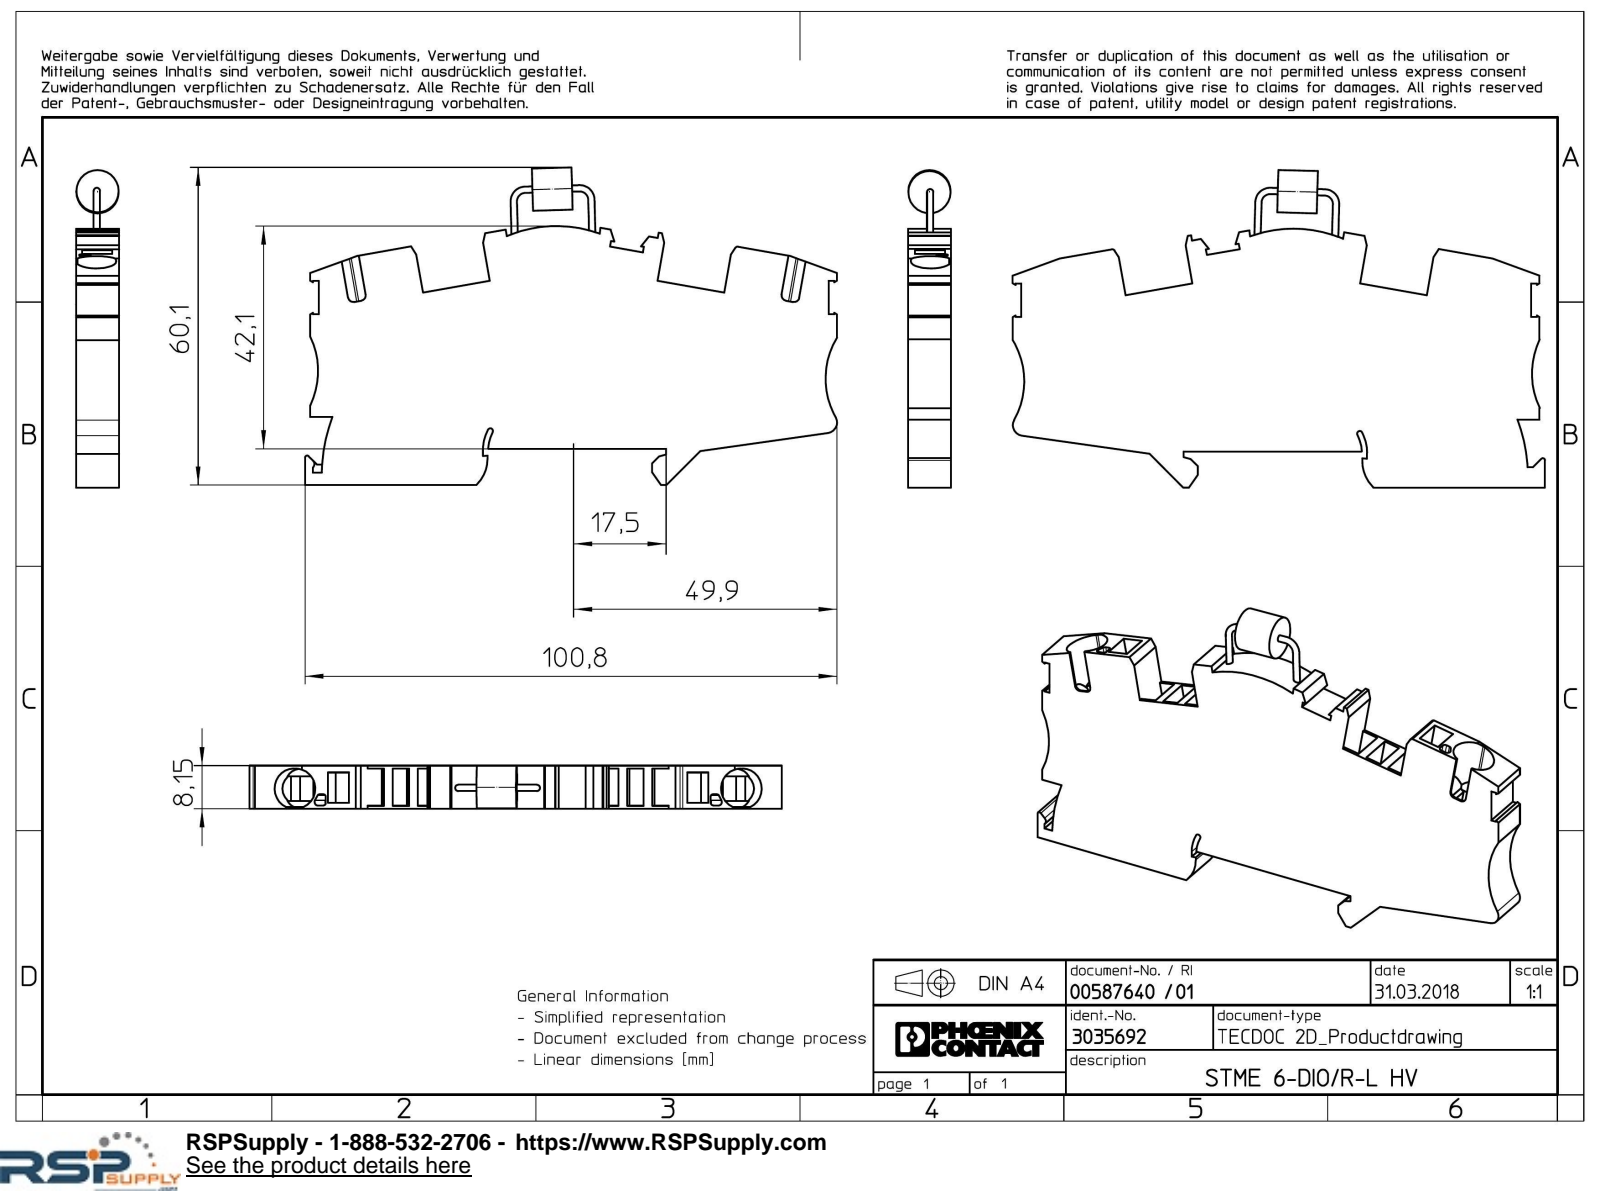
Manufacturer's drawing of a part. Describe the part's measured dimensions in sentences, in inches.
The part is named "STME-6-DIO_R-L-Select". Its 3-D file was written by "Creo Elements/Direct Modeling 18.1I 14-Aug-2016 (C) Parametric Technology GmbH (AUTOMOTIVE_DESIGN)". It is 1 solid with 184 faces: 147 planar, 33 cylindrical and 4 other. Overall it measures 3.969 by 2.366 by 0.321 inches. Its volume is 1.649 cubic inches and its surface area 21.9 square inches. Round bosses or shafts: 1 of diameter 0.315. Partial cylindrical surfaces (rounded edges, fillets, slot ends): 7 of radius 0.02, 4 of radius 0.039, 4 of radius 0.15, 2 of radius 0.026, 2 of radius 0.591, 2 of radius 0.945, 1 of radius 0.016, 1 of radius 0.024. The main face-to-face distances are 0.321, 0.191, 0.124, 0.067, 0.276, 0.022, 0.27, 0.298, 0.023, 0.298.
